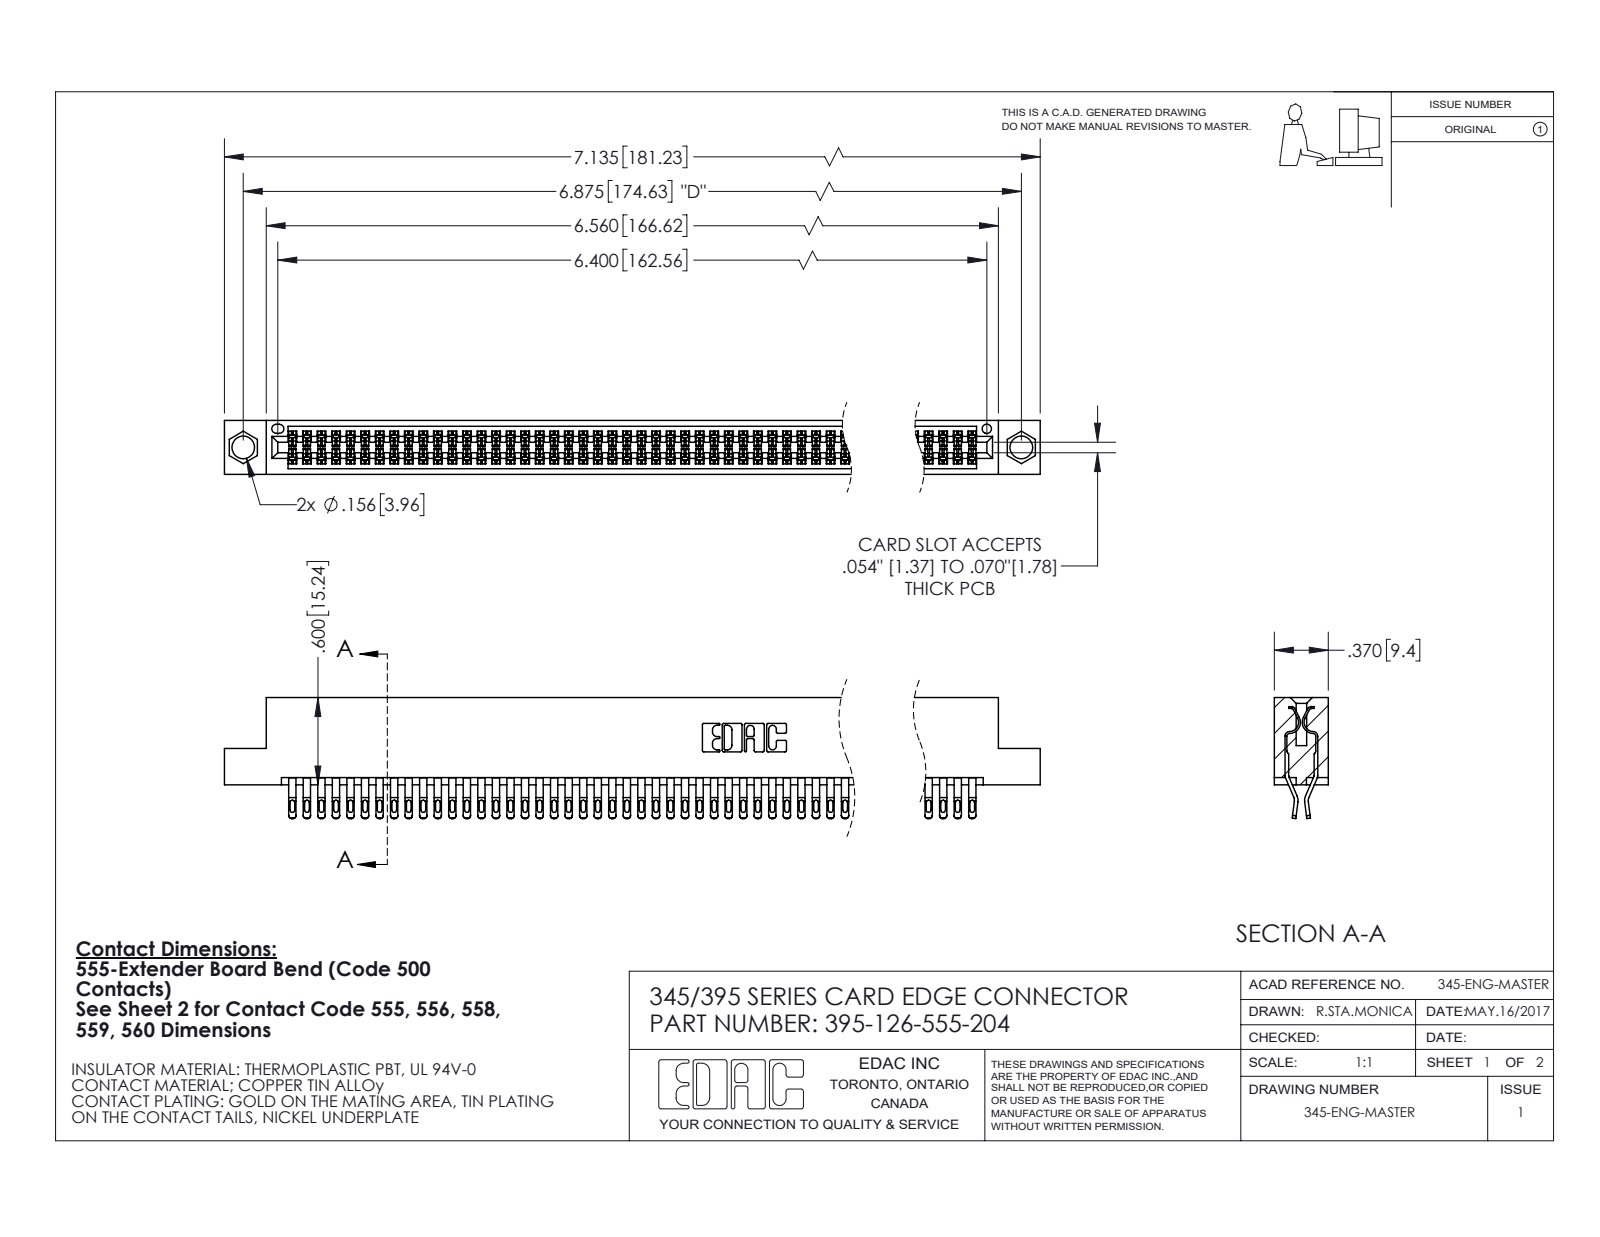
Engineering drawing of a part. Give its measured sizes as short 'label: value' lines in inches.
name: 345 Part_Flush Mounting Lugs - 0.156 Dia-TI; 395-126-555-204; 345-292-001_555 Tail
written by: SolidWorks 2020 (CONFIG_CONTROL_DESIGN)
unit: in
bodies: 127 solids, 7196 faces (4000 planar, 3196 cylindrical, 0 other)
size: 7.135 × 0.832 × 0.37
volume: 1.102 in³; area: 43.75 in²
holes: 2× ⌀0.156, 1× ⌀0.064
rounds: 315× R0.016, 252× R0.006, 252× R0.02, 22× R0.01, 6× R0.007, 6× R0.031, 3× R0.026, 2× R0.01
face distances: 0.298, 0.072, 0.025, 0.37, 0.2, 0.098, 0.272, 0.225, 0.175, 0.149
hole spacings: 0.27, 6.639, 6.875
